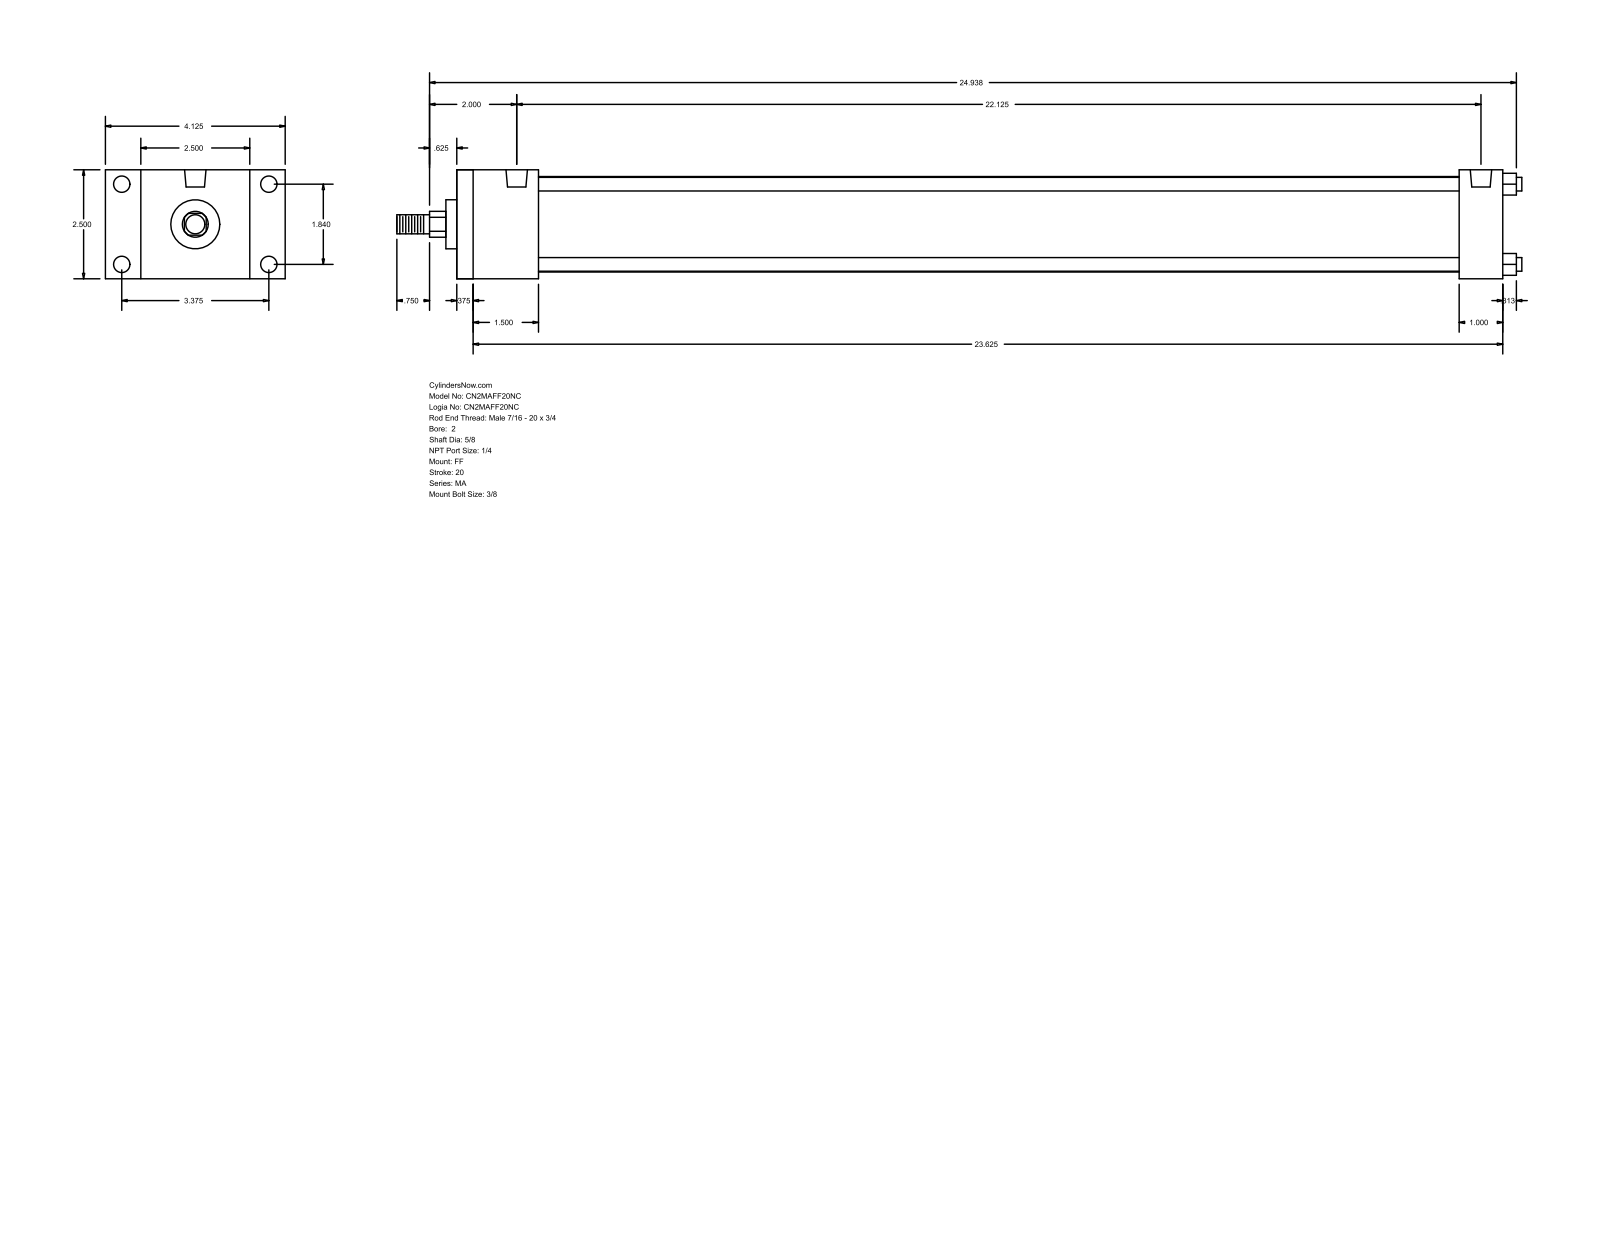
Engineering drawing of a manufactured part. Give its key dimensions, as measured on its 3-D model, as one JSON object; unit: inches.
{"part_name": "MA_FF__0200_0.625", "step_written_by": "GSSL Pune (CONFIG_CONTROL_DESIGN)", "units": "inches", "bodies": {"solids": 0, "faces": 92, "planar": 64, "cylindrical": 28, "other": 0}, "overall_size": [25.813, 4.125, 2.5], "round_holes": [[0.313, 4], [0.375, 4], [0.492, 2]], "round_bosses_or_shafts": [[0.313, 4], [2.19, 1], [1.125, 1], [0.625, 1], [0.437, 1]], "partial_cylinders_radius": [[0.297, 1]], "face_to_face_distances": [2.5, 24, 23.625, 0.375, 1, 1.5, 1.875, 23, 22.625, 21.125], "hole_center_spacings": [1.84, 3.375, 3.844, 22.125]}
